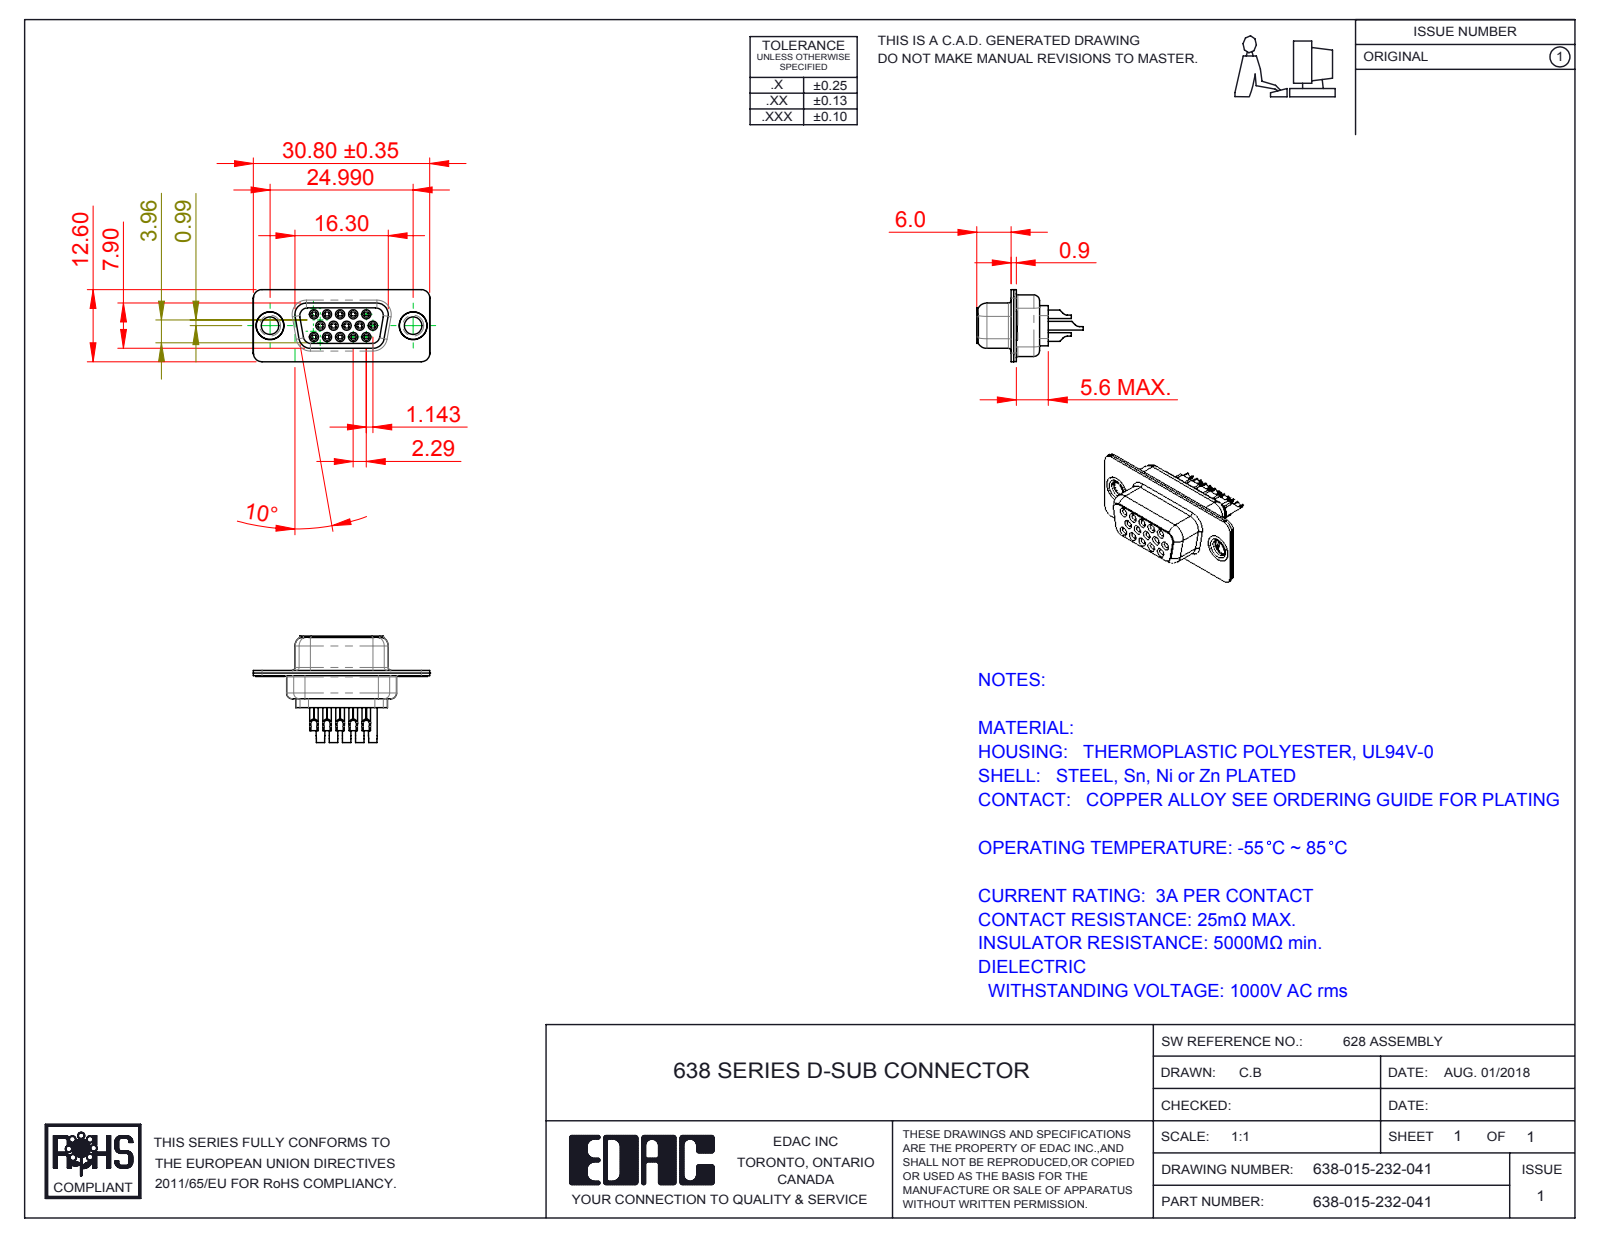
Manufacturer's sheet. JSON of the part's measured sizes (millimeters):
{"part_name": "638 Contact Row 3_32L; 638-015-232-041; 638 Thru Hole Rivet; 638 Shell Front_15 Contacts (+4 more)", "step_written_by": "SolidWorks 2016 (CONFIG_CONTROL_DESIGN)", "units": "millimeters", "bodies": {"solids": 20, "faces": 1588, "planar": 382, "cylindrical": 496, "other": 710}, "overall_size": [30.81, 18.6, 12.6], "volume_mm3": 1525, "surface_area_mm2": 5715, "round_holes": [[0.8, 15], [1, 15], [1.1, 15], [1.6, 15], [1.7, 15], [1.8, 15], [2, 2], [3.05, 2], [4, 2], [4.05, 2], [4.85, 2]], "round_bosses_or_shafts": [[2, 15], [1.5, 15], [1.2, 15], [5, 2], [4.95, 2], [4.8, 2], [3.55, 2]], "partial_cylinders_radius": [[1.5, 20], [2, 12], [0.28, 10], [1.55, 8], [1, 7], [1.35, 5], [0.25, 4], [0.5, 4]], "face_to_face_distances": [0.45, 0.9, 0.4, 1.43, 8.88, 6.6, 1.4, 2.28, 7.05, 0.85], "hole_center_spacings": [3.96, 2.28, 4.57, 2.29, 6.05, 6.04, 6.86, 7.92]}
